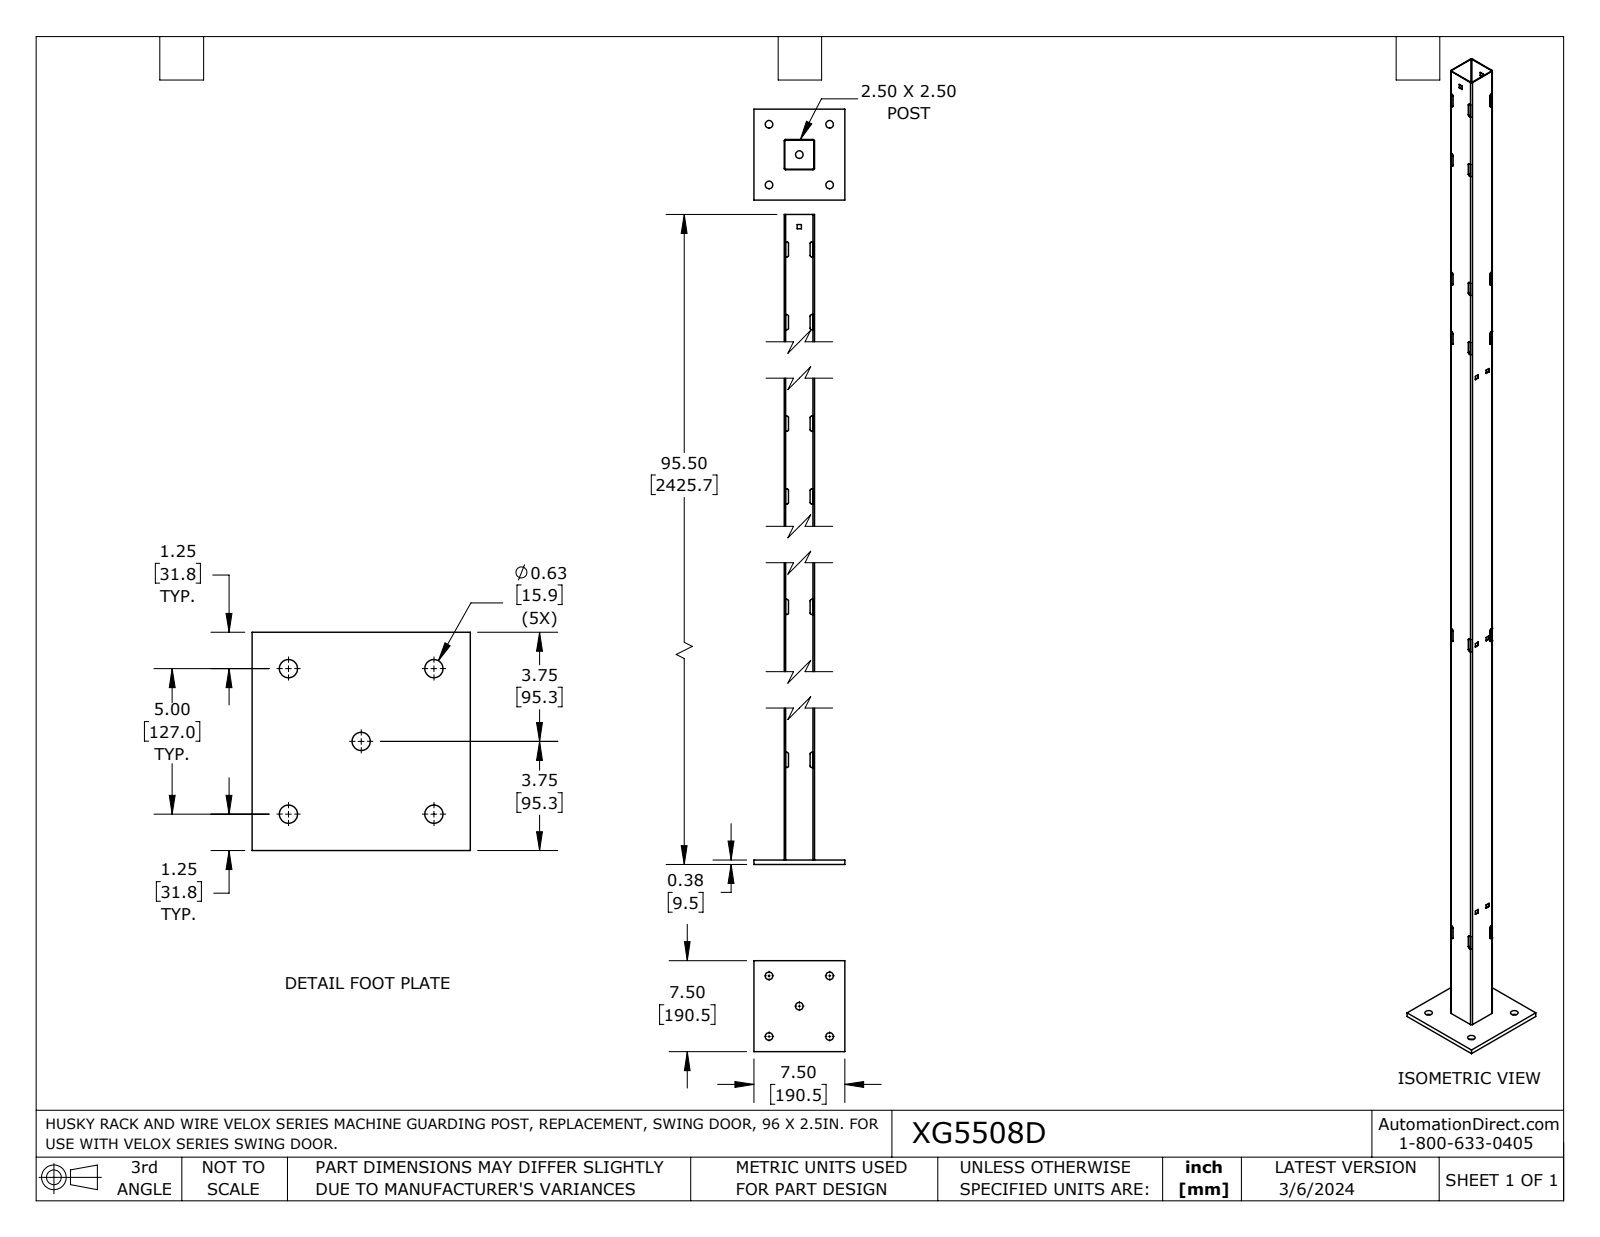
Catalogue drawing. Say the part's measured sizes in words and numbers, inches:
The part is named "XG5508D_Default". Its 3-D file was written by "SolidWorks 2023 (CONFIG_CONTROL_DESIGN)". It is 2 solids with 217 faces: 160 planar, 57 cylindrical and 0 other. Overall it measures 95.5 by 7.5 by 7.5 inches. Its volume is 73.05 cubic inches and its surface area 1 942 square inches. Round holes: 5 of diameter 0.625. Partial cylindrical surfaces (rounded edges, fillets, slot ends): 34 of radius 0.13, 4 of radius 0.062, 4 of radius 0.12. The main face-to-face distances are 0.058, 2.442, 2.5, 2.384, 0.375, 2.558, 4.942, 5, 7.5, 2.342. The hole center spacings are 3.535, 5, 7.071.
